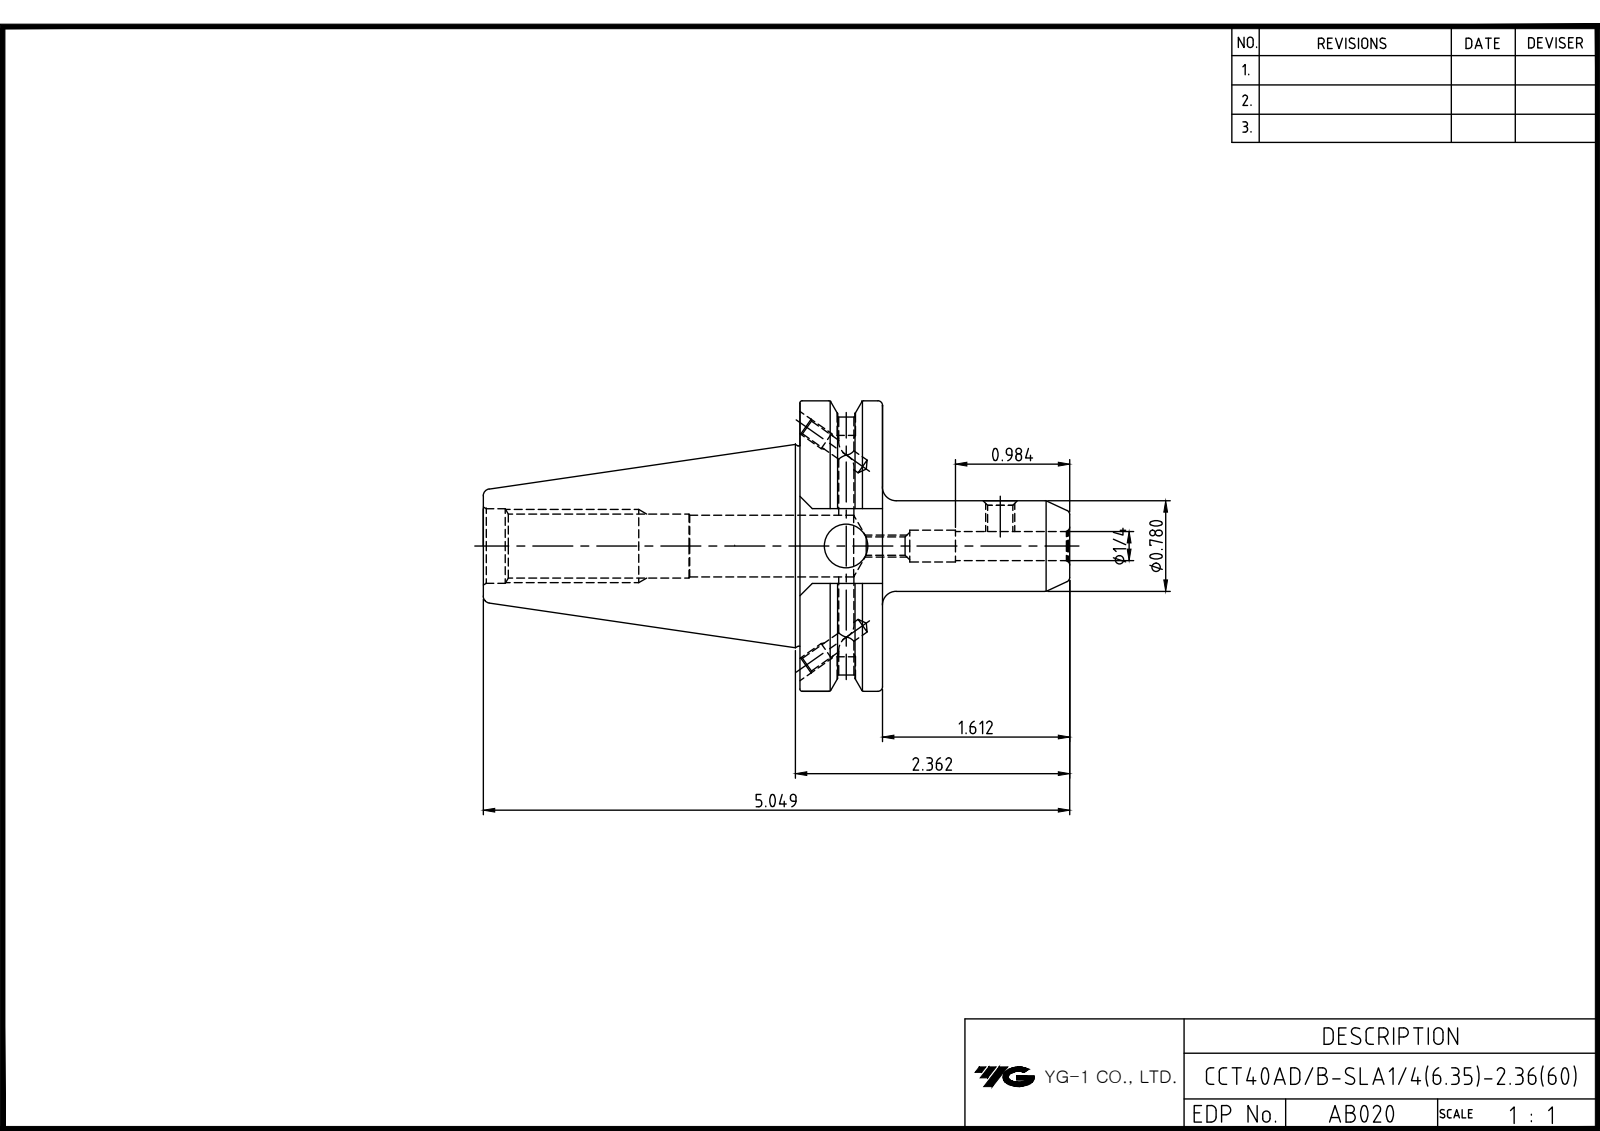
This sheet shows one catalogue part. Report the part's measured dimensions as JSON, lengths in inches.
{"part_name": "LO-CCT40ADB-SLA6.35-60", "step_written_by": "Autodesk Inventor 2025 (AUTOMOTIVE_DESIGN)", "units": "inches", "bodies": {"solids": 1, "faces": 92, "planar": 39, "cylindrical": 29, "other": 24}, "overall_size": [5.049, 2.5, 2.405], "volume_in3": 7.012, "surface_area_in2": 37.62, "round_holes": [[0.128, 4], [0.157, 2], [0.165, 2], [0.156, 1], [0.211, 1], [0.25, 1], [0.297, 1], [0.375, 1], [0.527, 1], [0.642, 1]], "round_bosses_or_shafts": [[2.5, 1], [1.724, 1], [0.78, 1]], "partial_cylinders_radius": [[1.108, 1]], "face_to_face_distances": [0.711, 1.874, 0.645, 2.726, 3.437, 3.2, 0.474, 0.237, 3.05, 0.323]}
